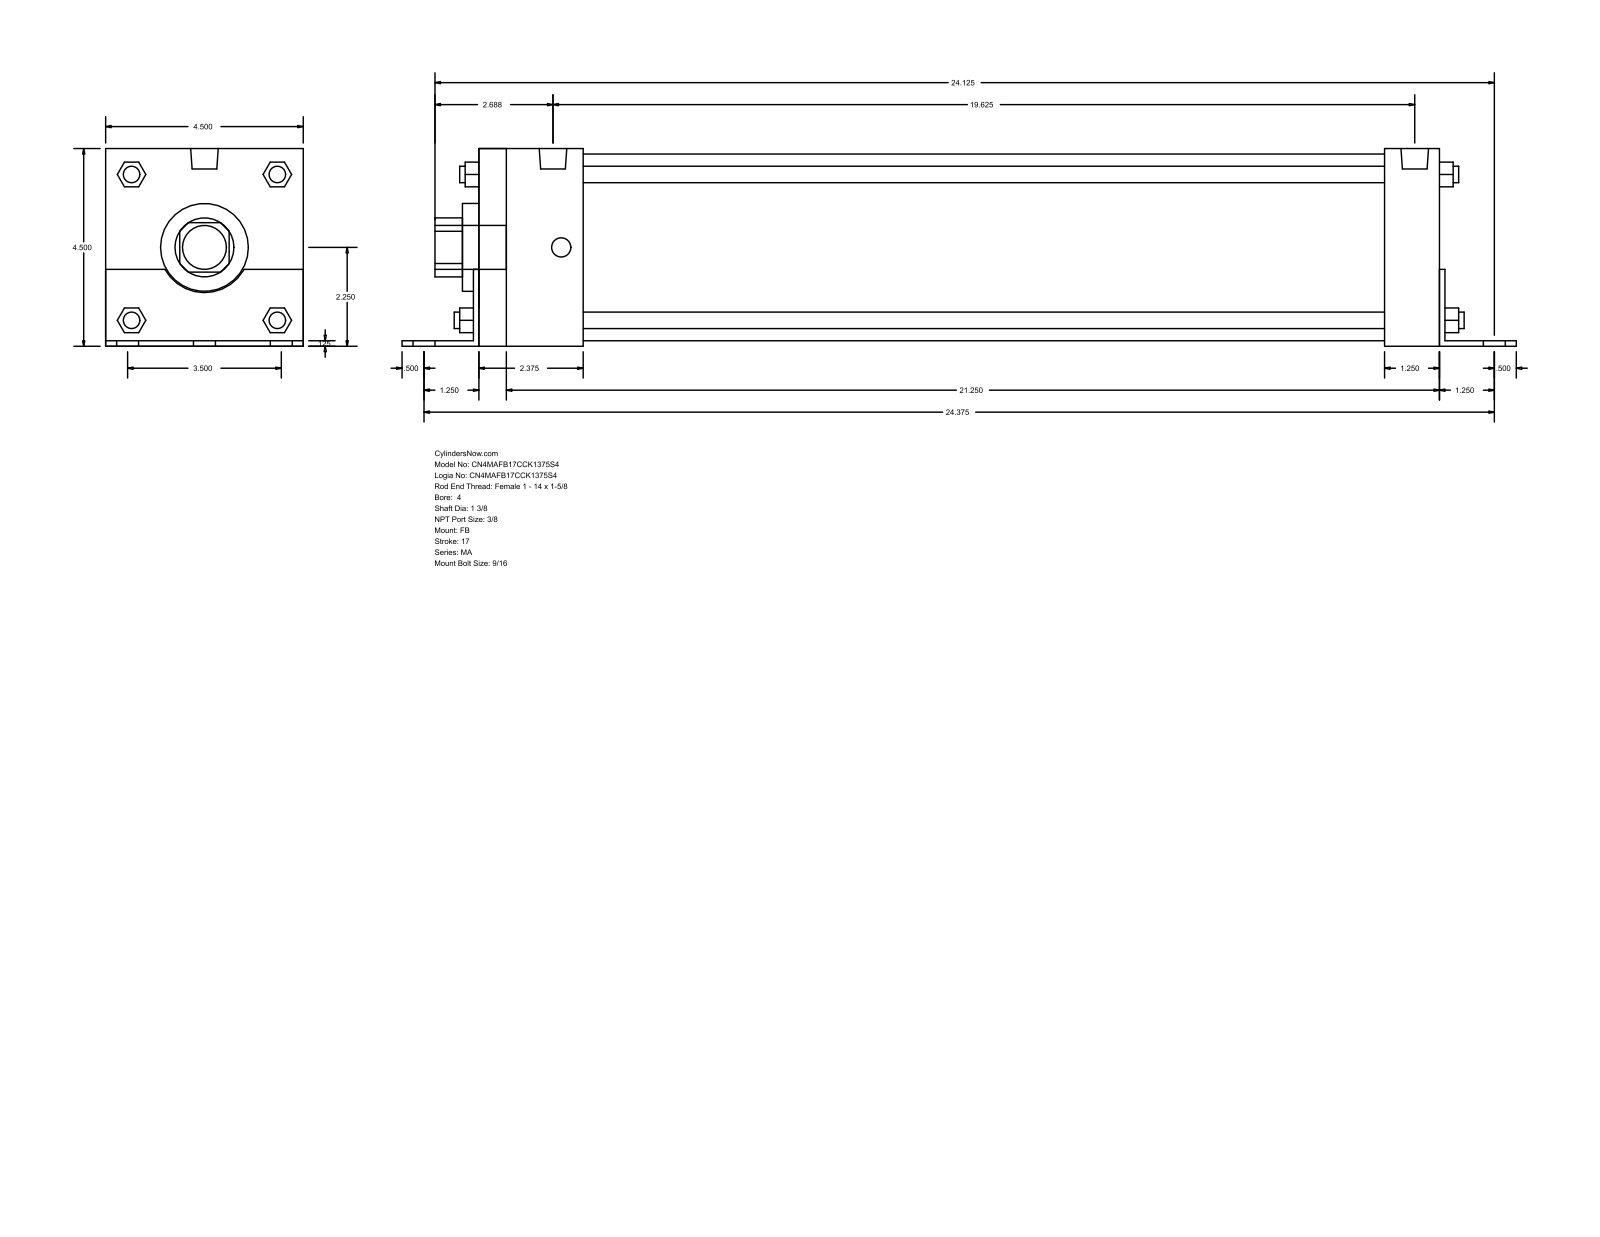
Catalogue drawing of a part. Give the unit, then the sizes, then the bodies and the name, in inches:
Units: inches
Overall size (bounding box): 25.375 × 4.502 × 4.5
Round holes (diameter × count): ⌀1.375 ×1, ⌀2 ×1, ⌀4.25 ×1
Round bosses / shafts (diameter × count): ⌀0.563 ×6, ⌀0.437 ×4, ⌀0.375 ×4, ⌀0.627 ×2, ⌀1 ×1
Partial cylindrical surfaces — rounded edges, fillets, slot ends (radius × count): R0.672 ×1, R1.03 ×1
Main face-to-face distances: 4.5, 0.125, 4.502, 0.123, 4.377, 21.875, 0.125, 22, 1.375, 2.375
Bodies: 0 solids, 140 faces (105 planar, 35 cylindrical, 0 other)
Part name (STEP PRODUCT): MA_FB__0400_1.375
STEP written by: GSSL Pune (CONFIG_CONTROL_DESIGN)
